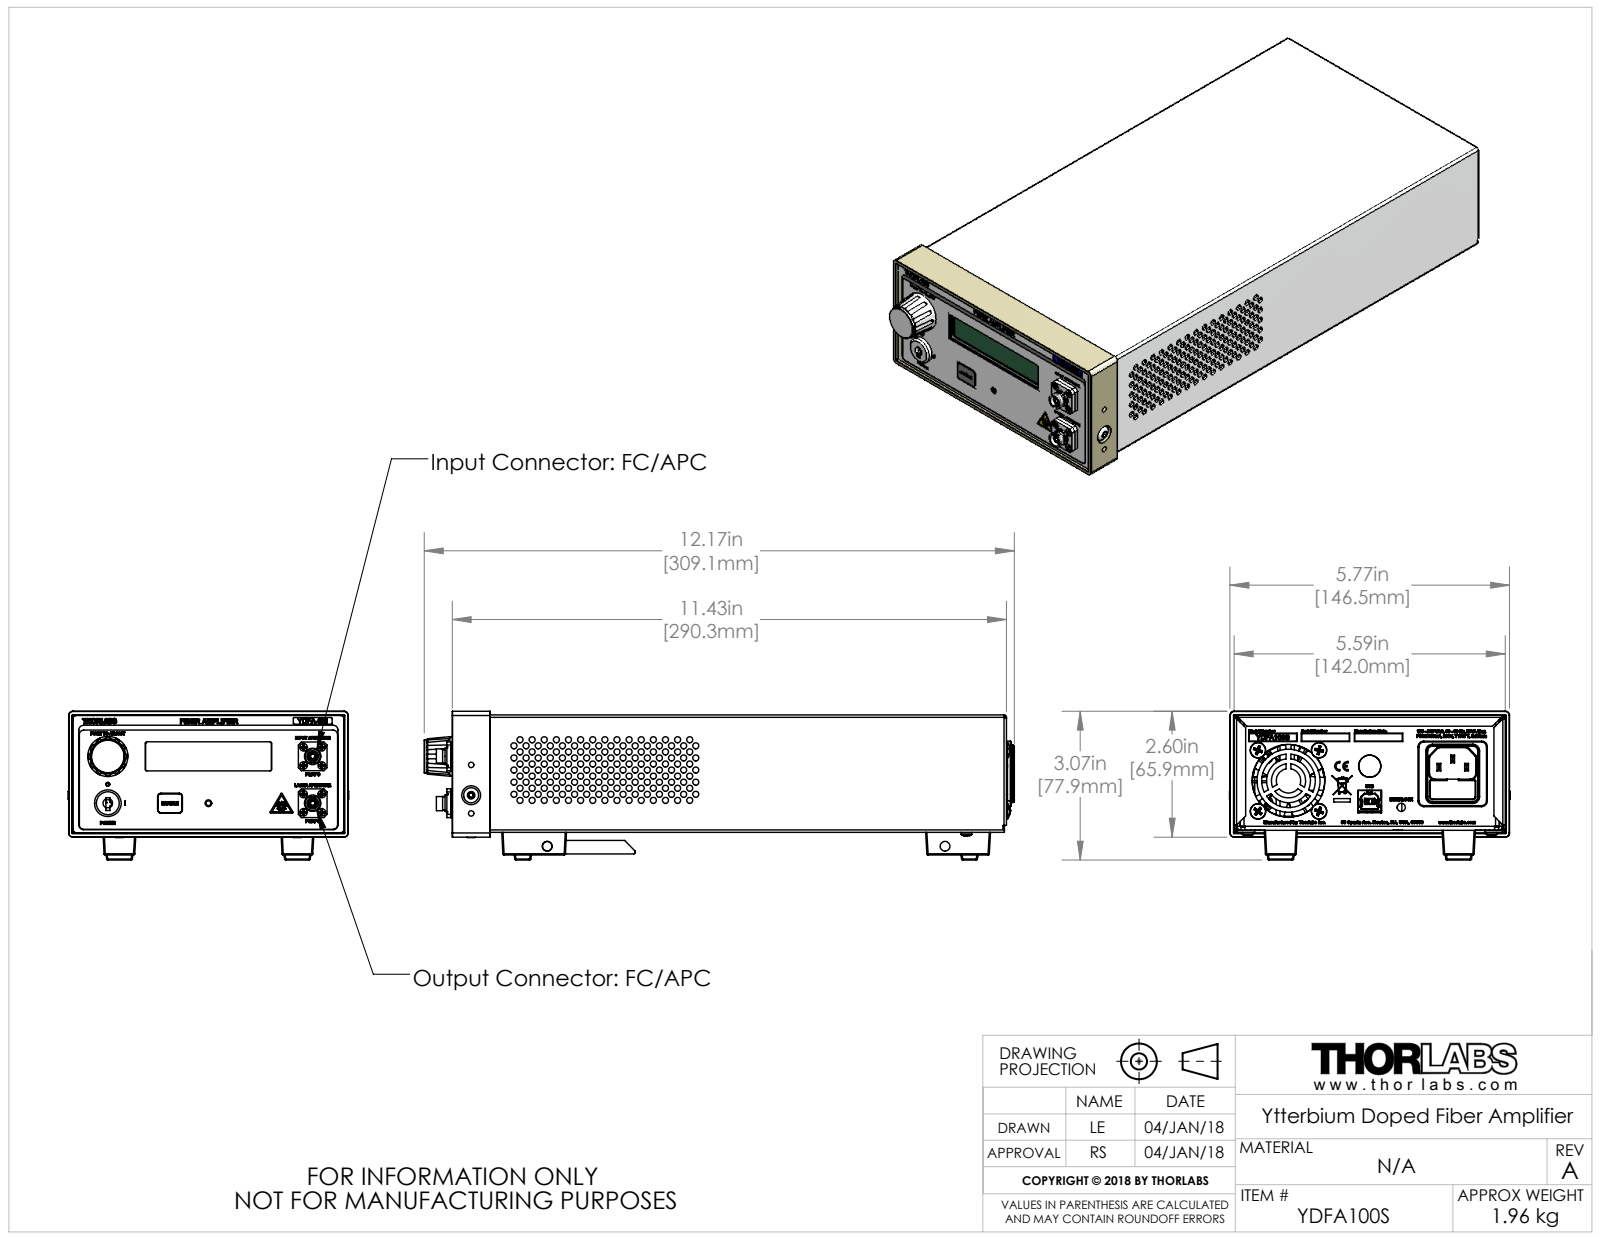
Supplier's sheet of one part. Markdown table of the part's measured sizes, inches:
| quantity | value |
| --- | --- |
| part name | YDFA-SM-E0W |
| STEP written by | SolidWorks 2016 (AUTOMOTIVE_DESIGN) |
| units | inches |
| bodies | 0 solids, 8824 faces (4480 planar, 2086 cylindrical, 2258 other) |
| overall size | 12.17 × 5.786 × 3.069 |
| round holes (diameter × count) | 0.125 × 171, 0.037 × 42, 0.039 × 16, 0.097 × 12, 0.157 × 12, 0.07 × 8, 0.087 × 8, 0.087 × 8, 0.112 × 8, 0.12 × 8, 0.122 × 8, 0.165 × 8 |
| round bosses / shafts (diameter × count) | 0.165 × 12, 0.161 × 12, 0.153 × 12, 0.167 × 8, 0.164 × 8, 0.12 × 8, 0.086 × 8, 0.018 × 6 |
| partial cylindrical surfaces (radius × count) | 0.02 × 51, 0.025 × 48, 0.005 × 32, 0.01 × 20, 0.05 × 17, 0.01 × 15, 0.118 × 14, 0.039 × 12 |
| main face-to-face distances | 0.04, 0.062, 2.377, 2.337, 2.276, 2.315, 5.55, 0.057, 0.018, 5.532 |
| hole center spacings | 0.559, 0.25, 0.5, 0.354, 0.791, 0.902, 0.75, 0.707 |
